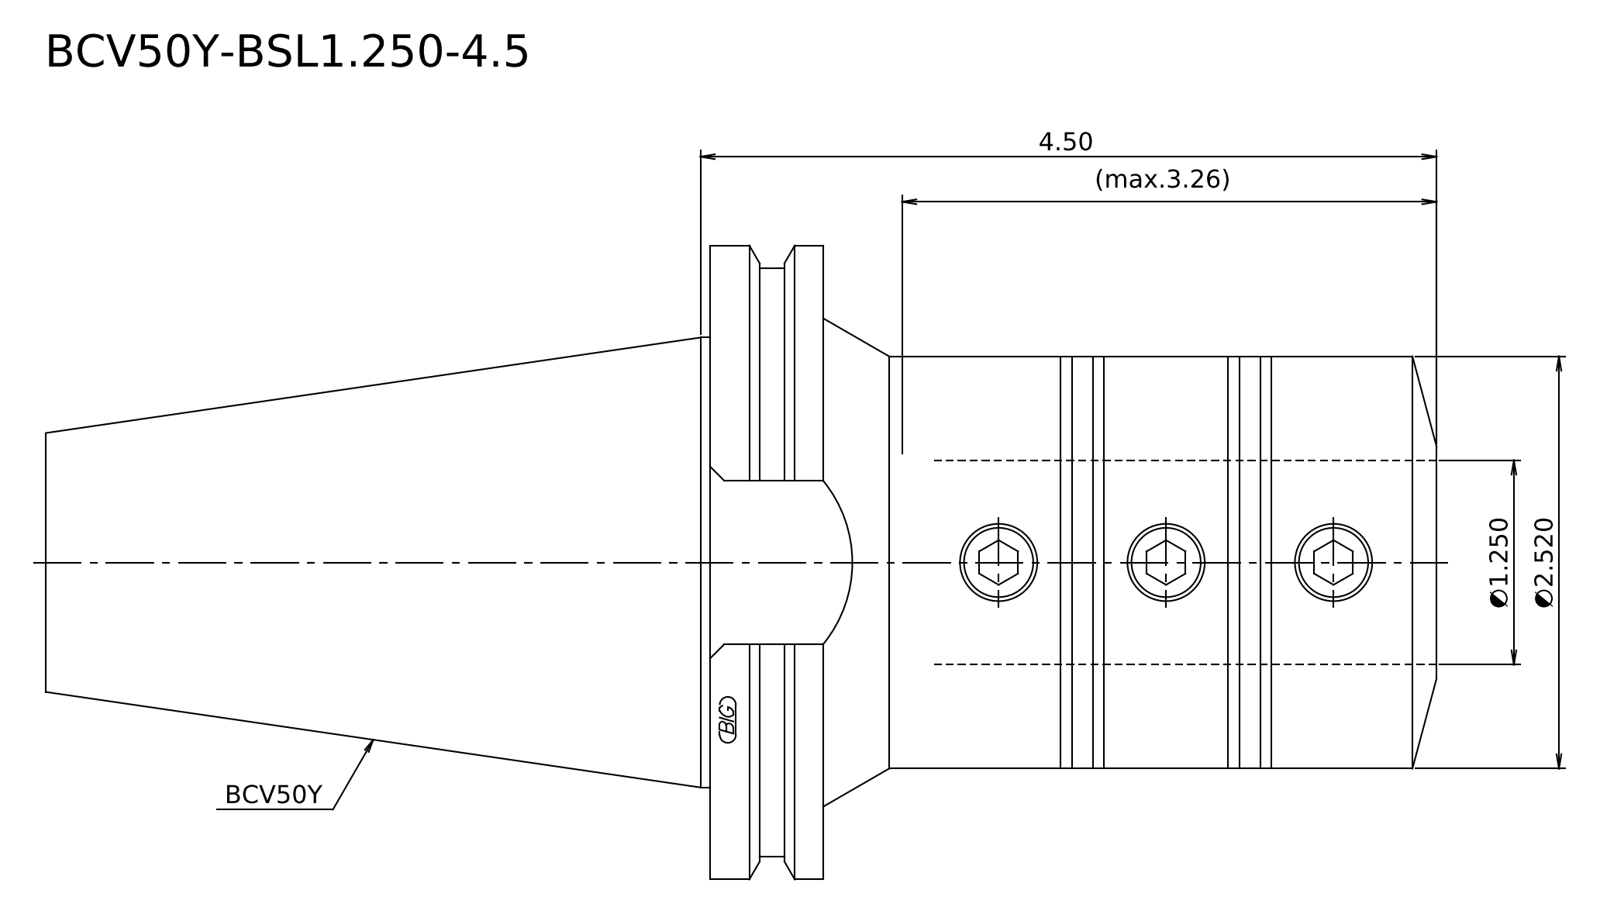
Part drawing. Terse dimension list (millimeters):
written by: Kubotek KeyCreator 2011 V10.0.2 (22737) (automotive_design)
unit: mm
bodies: 1 solid, 16 faces (6 planar, 5 cylindrical, 5 other)
size: 215.9 × 98.42 × 98.42
volume: 689 738 mm³; area: 55 182 mm²
bosses: 1× ⌀98.42, 1× ⌀91.29, 1× ⌀69.85, 1× ⌀64
face distances: 17.55, 120.65, 103.1, 95.25, 112.8, 215.9, 101.26, 6.01, 11.54, 114.64
